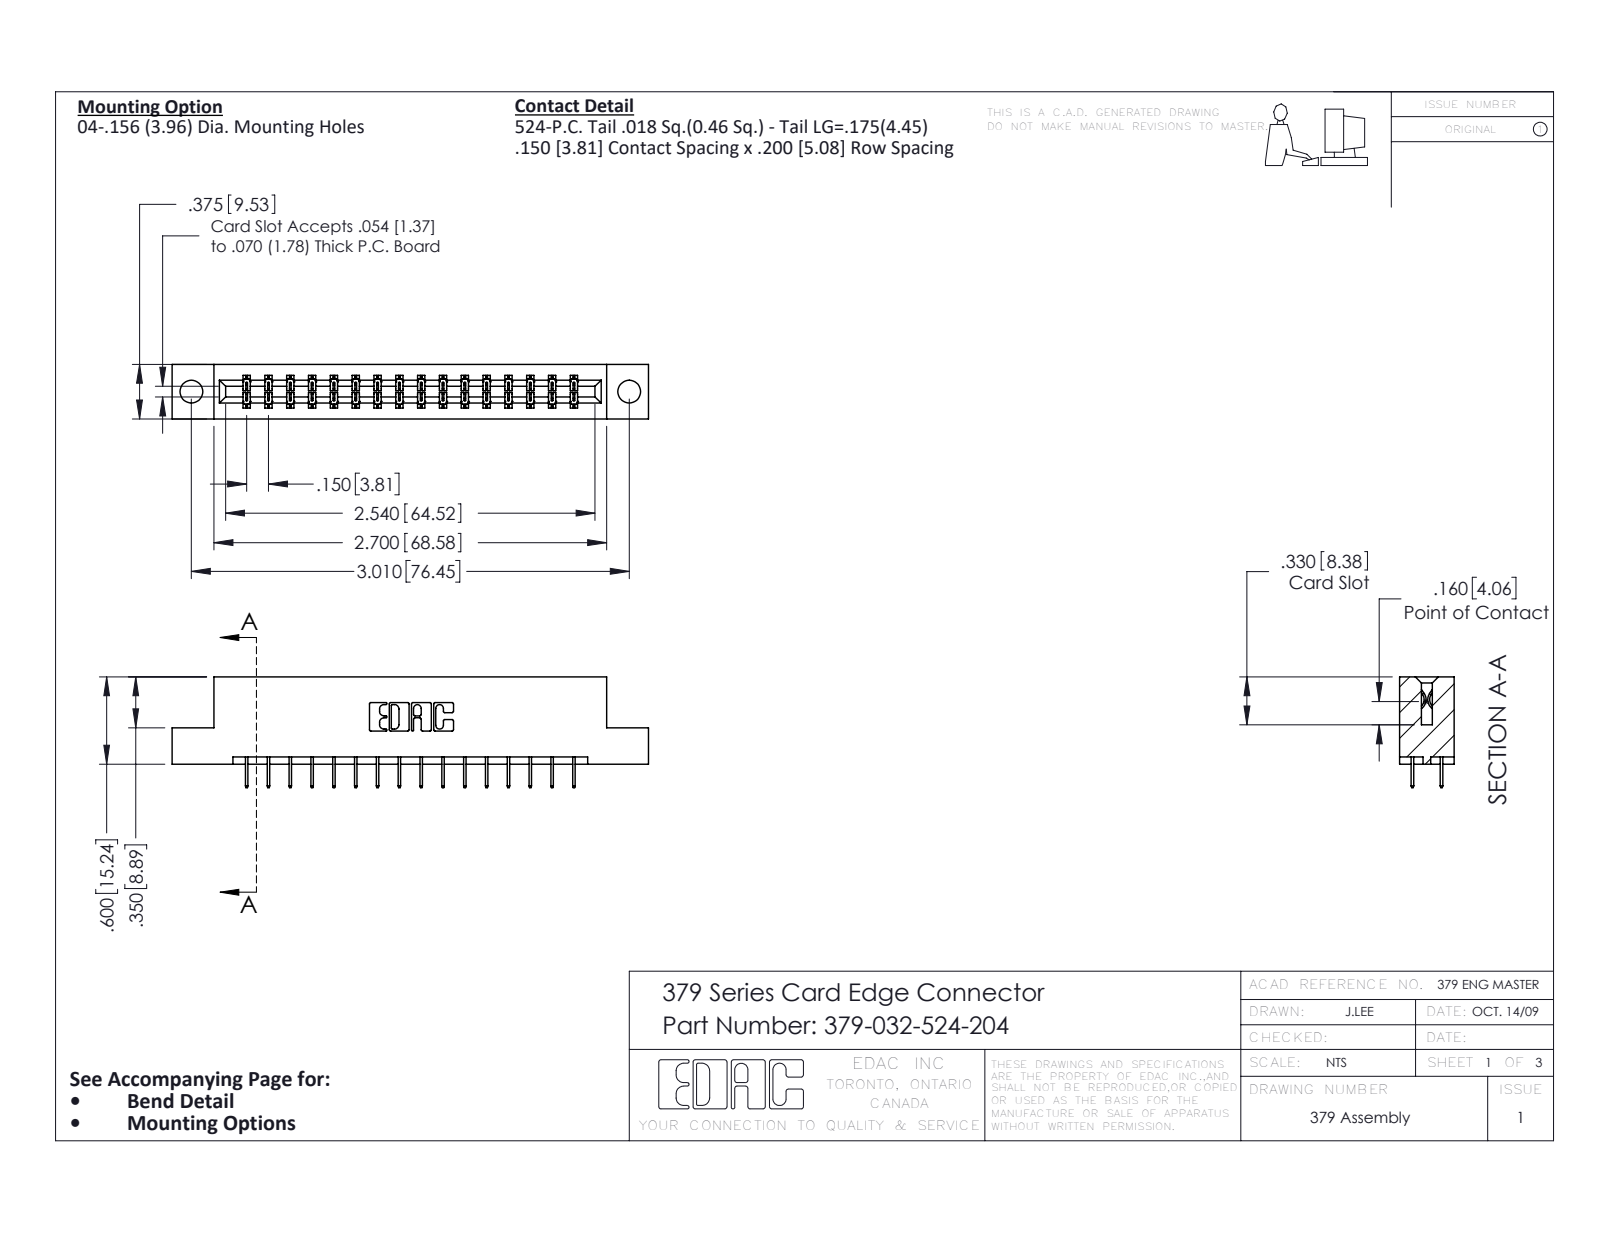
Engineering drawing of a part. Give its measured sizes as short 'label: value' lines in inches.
name: 379-032-524-204; 379 Part_Flush - .156 Dia - TH; 345-292-001_345-293-124
written by: SolidWorks 2020 (CONFIG_CONTROL_DESIGN)
unit: in
bodies: 33 solids, 1906 faces (1414 planar, 492 cylindrical, 0 other)
size: 3.275 × 0.762 × 0.375
volume: 0.513 in³; area: 13.7 in²
holes: 2× ⌀0.156
rounds: 63× R0.006, 22× R0.01, 6× R0.007, 6× R0.031, 3× R0.026, 2× R0.014, 2× R0.022, 2× R0.024
face distances: 0.3, 0.375, 0.075, 0.2, 0.1, 0.15, 0.05, 0.6, 0.225, 0.55
hole spacings: 3.01
